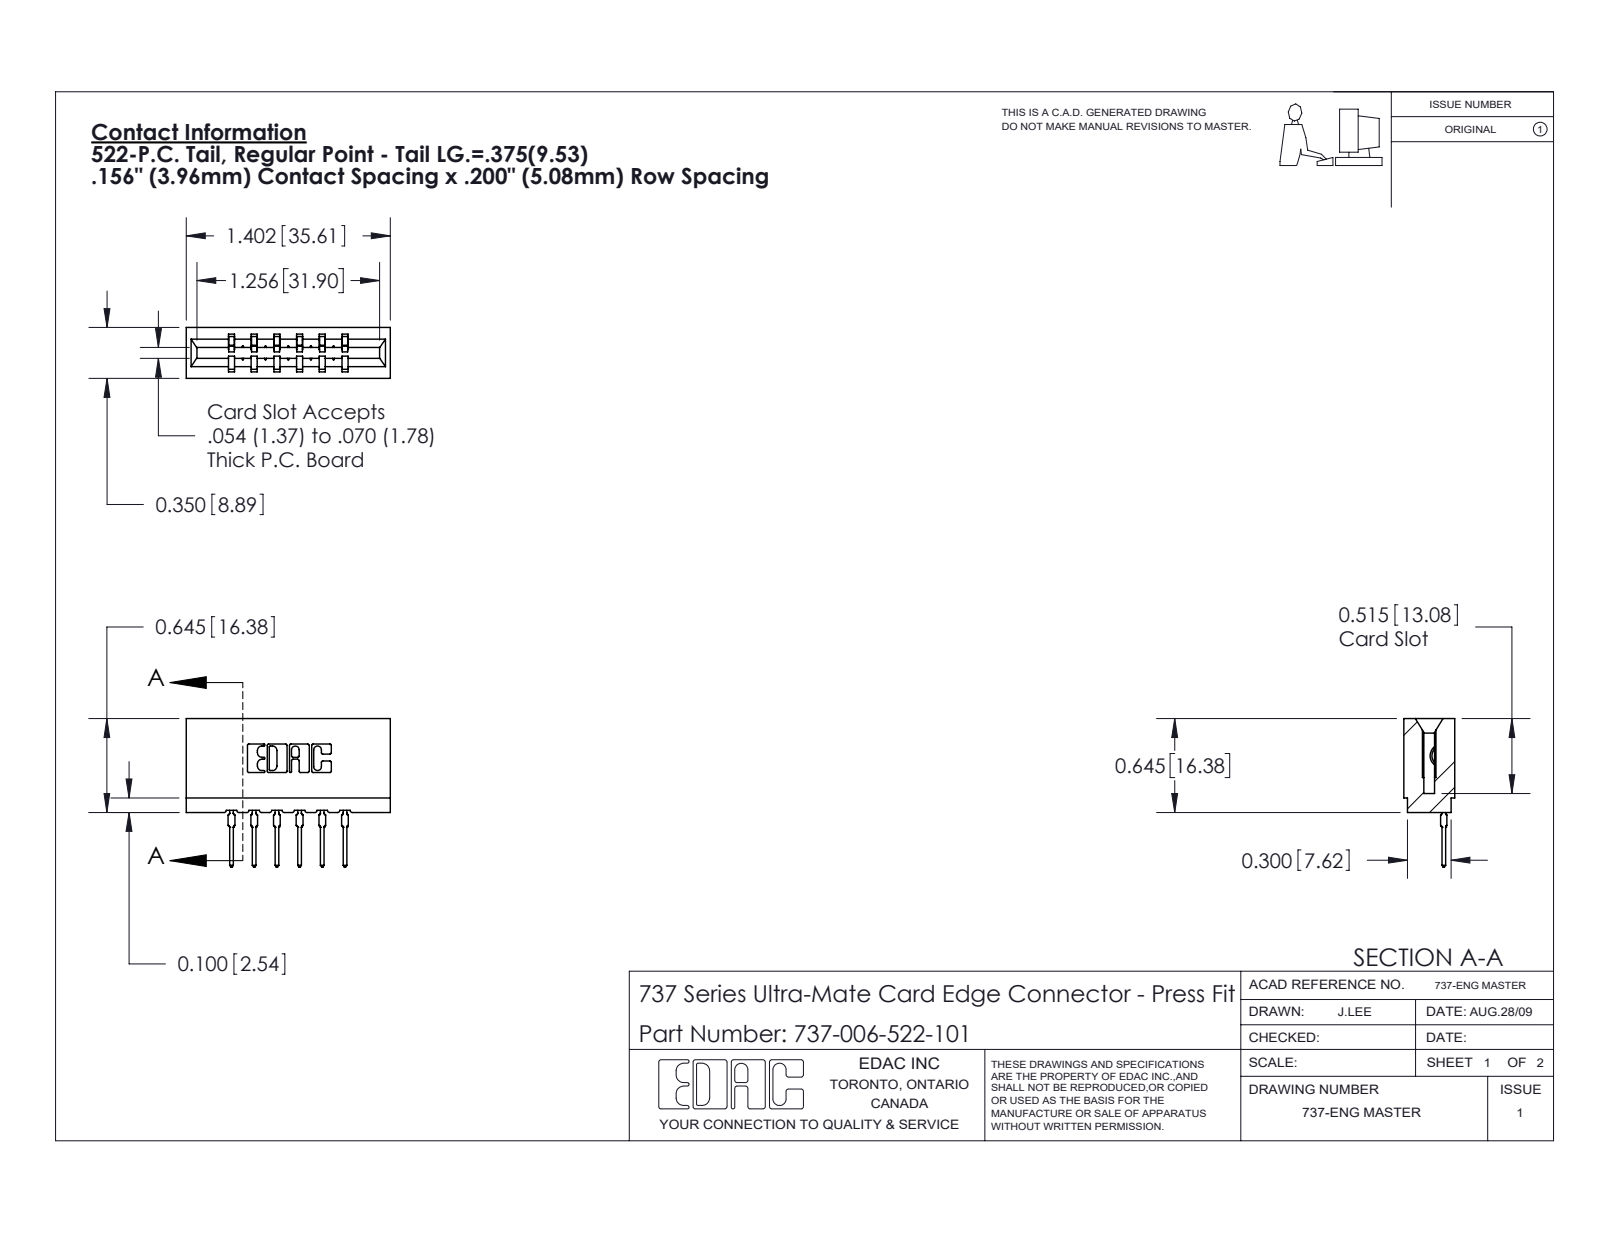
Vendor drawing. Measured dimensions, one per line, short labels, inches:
name: 737-006-522-101; 737 Part_Insulator Option - 01; 745-292-001_522
written by: SolidWorks 2020 (CONFIG_CONTROL_DESIGN)
unit: in
bodies: 7 solids, 772 faces (462 planar, 154 cylindrical, 156 other)
size: 1.402 × 1.021 × 0.35
volume: 0.226 in³; area: 6.687 in²
rounds: 22× R0.01, 12× R0.015, 12× R0.021, 6× R0.007, 6× R0.031, 4× R0.005, 4× R0.011, 3× R0.026
face distances: 0.156, 0.138, 0.212, 0.35, 0.312, 0.354, 0.198, 0.074, 0.468, 0.27
